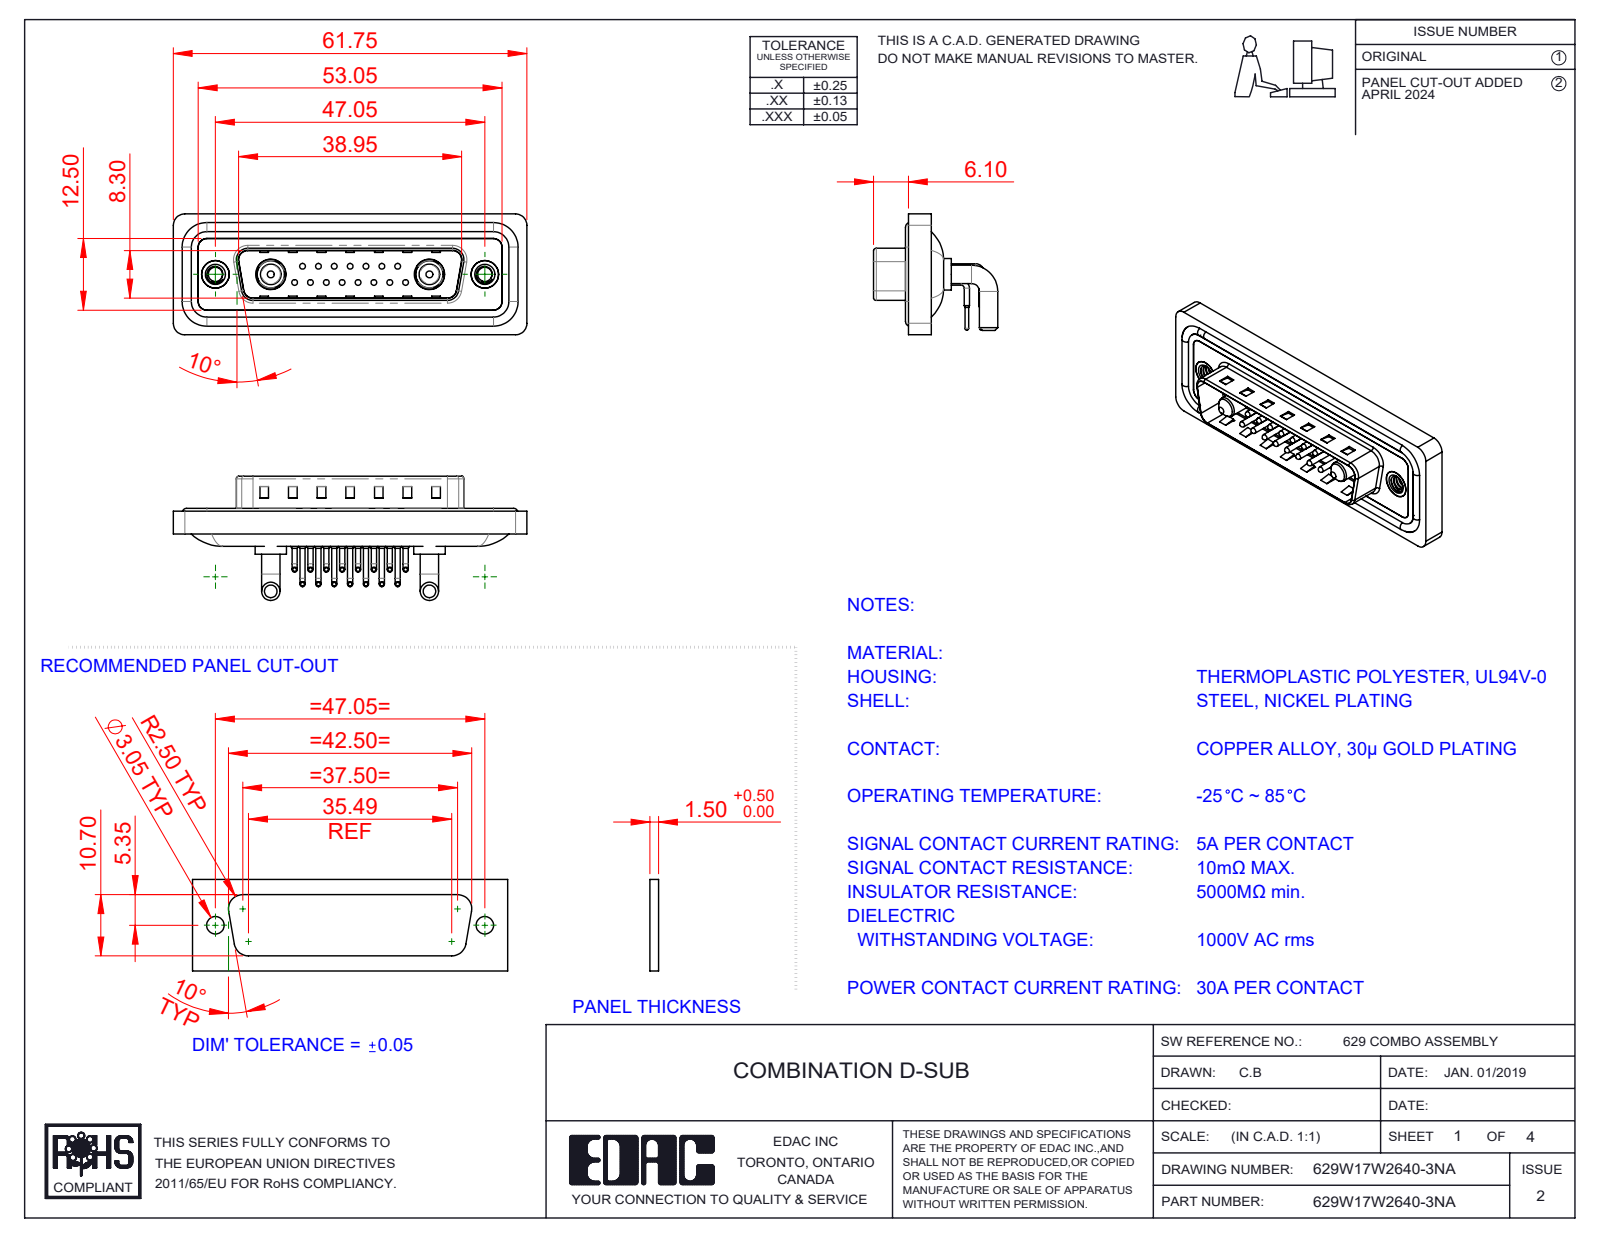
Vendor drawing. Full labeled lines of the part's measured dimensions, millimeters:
Part name (STEP PRODUCT): 629Combo Contact Row 2; 629Combo Contact Row 1; 629Combo Housing_17W2; Power Pin_30A RA (+5 more)
STEP written by: SolidWorks 2023 (CONFIG_CONTROL_DESIGN)
Units: millimetres
Bodies: 26 solids, 2213 faces (1189 planar, 768 cylindrical, 256 other)
Overall size (bounding box): 61.75 × 21.7 × 21.1
Volume: 7 572 mm³ · Surface area: 12 642 mm²
Round holes (diameter × count): ⌀0.75 ×15, ⌀1.6 ×15, ⌀2 ×15, ⌀2.5 ×2, ⌀4 ×2, ⌀4.8 ×2, ⌀4.85 ×2, ⌀5 ×2, ⌀5.3 ×2
Round bosses / shafts (diameter × count): ⌀0.9 ×30, ⌀1.5 ×15, ⌀1 ×15, ⌀0.65 ×15, ⌀3.2 ×4, ⌀1.6 ×4, ⌀5.5 ×2, ⌀5.2 ×2
Partial cylindrical surfaces — rounded edges, fillets, slot ends (radius × count): R1.5 ×18, R2 ×18, R1.01 ×15, R0.5 ×8, R1.6 ×8, R0.25 ×4, R0.6 ×4, R0.65 ×4
Main face-to-face distances: 0.4, 2.9, 0.8, 4.1, 1.1, 2.1, 1.6, 4.5, 1.5, 2.5
Hole centre spacings: 3.16, 2.77, 5.54, 8.31, 5.04, 7.49, 11.08, 5.03
